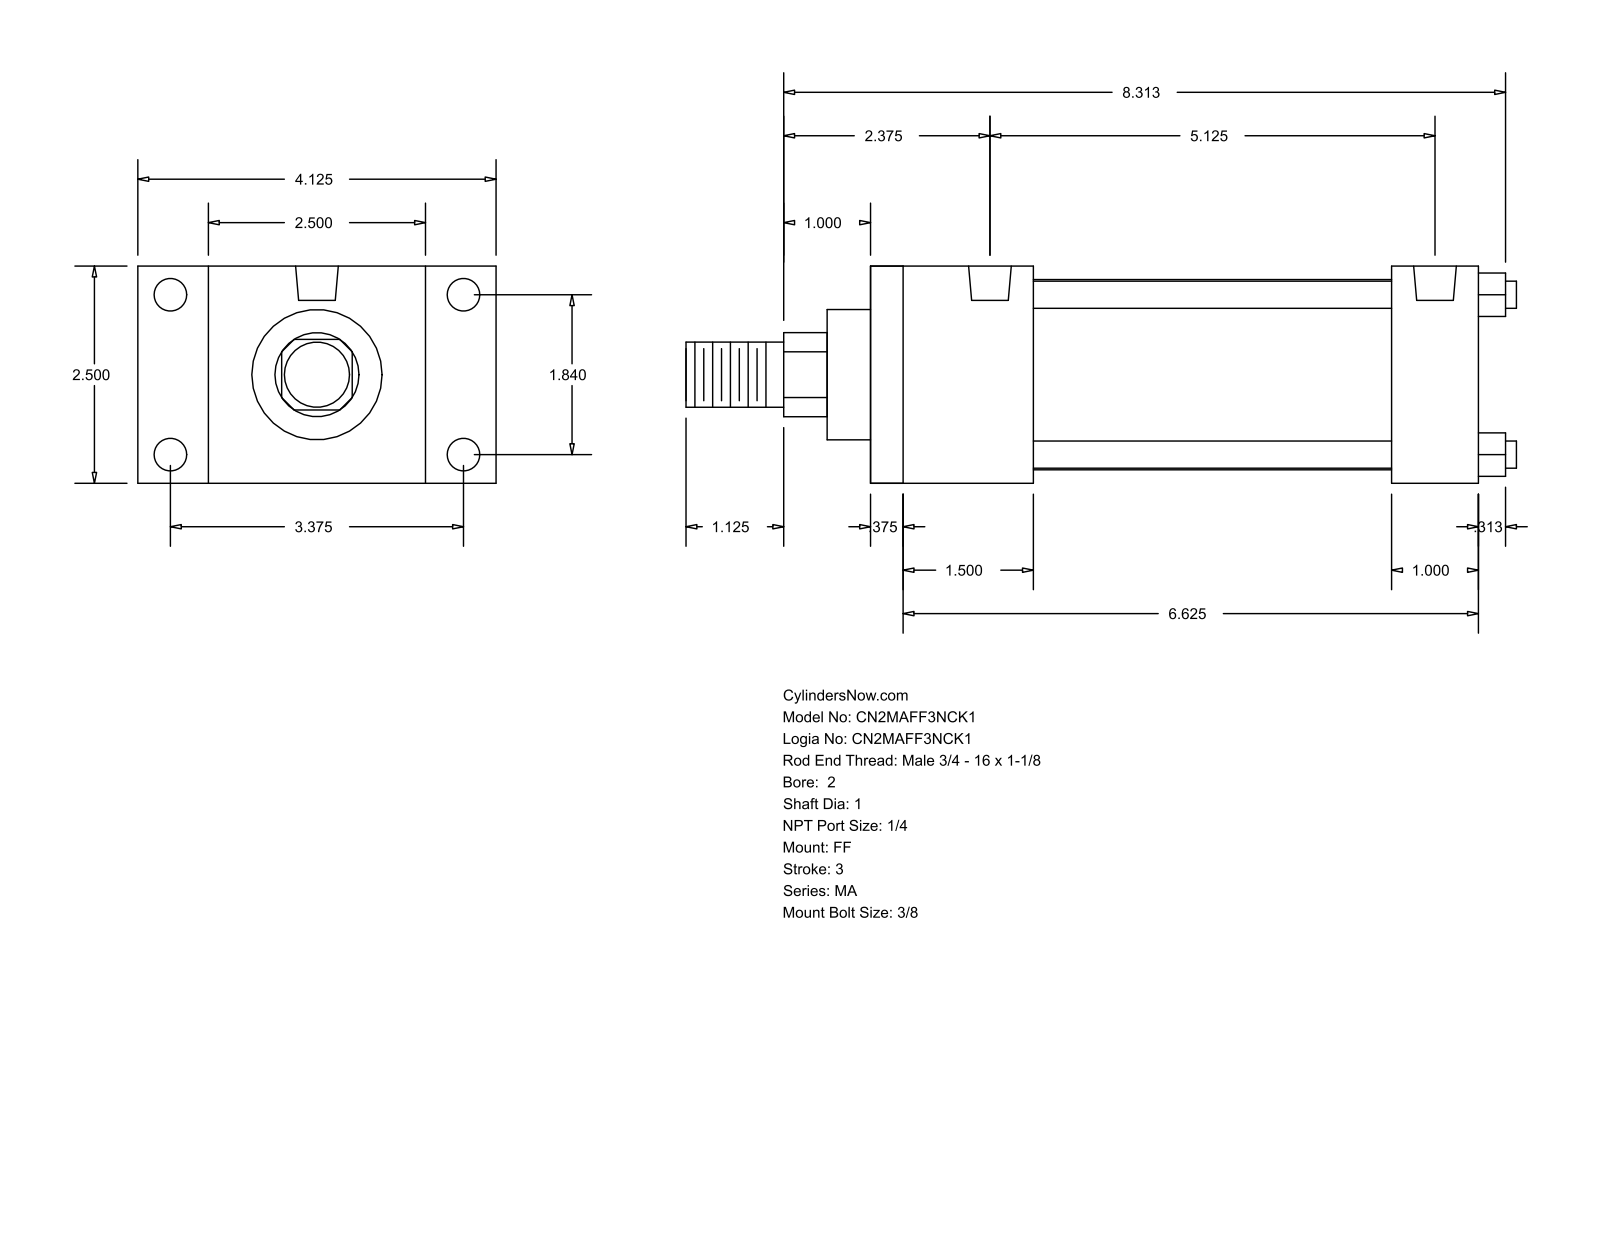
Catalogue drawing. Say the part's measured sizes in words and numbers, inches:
The part is named "MA_FF__0200_1". Its 3-D file was written by "GSSL Pune (CONFIG_CONTROL_DESIGN)". It is 0 solids with 92 faces: 64 planar, 28 cylindrical and 0 other. Overall it measures 9.563 by 4.125 by 2.5 inches. Round holes: 4 of diameter 0.313, 4 of diameter 0.375, 2 of diameter 0.492. Round bosses or shafts: 4 of diameter 0.313, 1 of diameter 2.19, 1 of diameter 1.5, 1 of diameter 1, 1 of diameter 0.75. Partial cylindrical surfaces (rounded edges, fillets, slot ends): 1 of radius 0.484. The main face-to-face distances are 2.5, 7, 0.375, 6.625, 1, 0.813, 0.5, 1.875, 6, 1.5. The hole center spacings are 1.84, 3.375, 3.844, 5.125.
